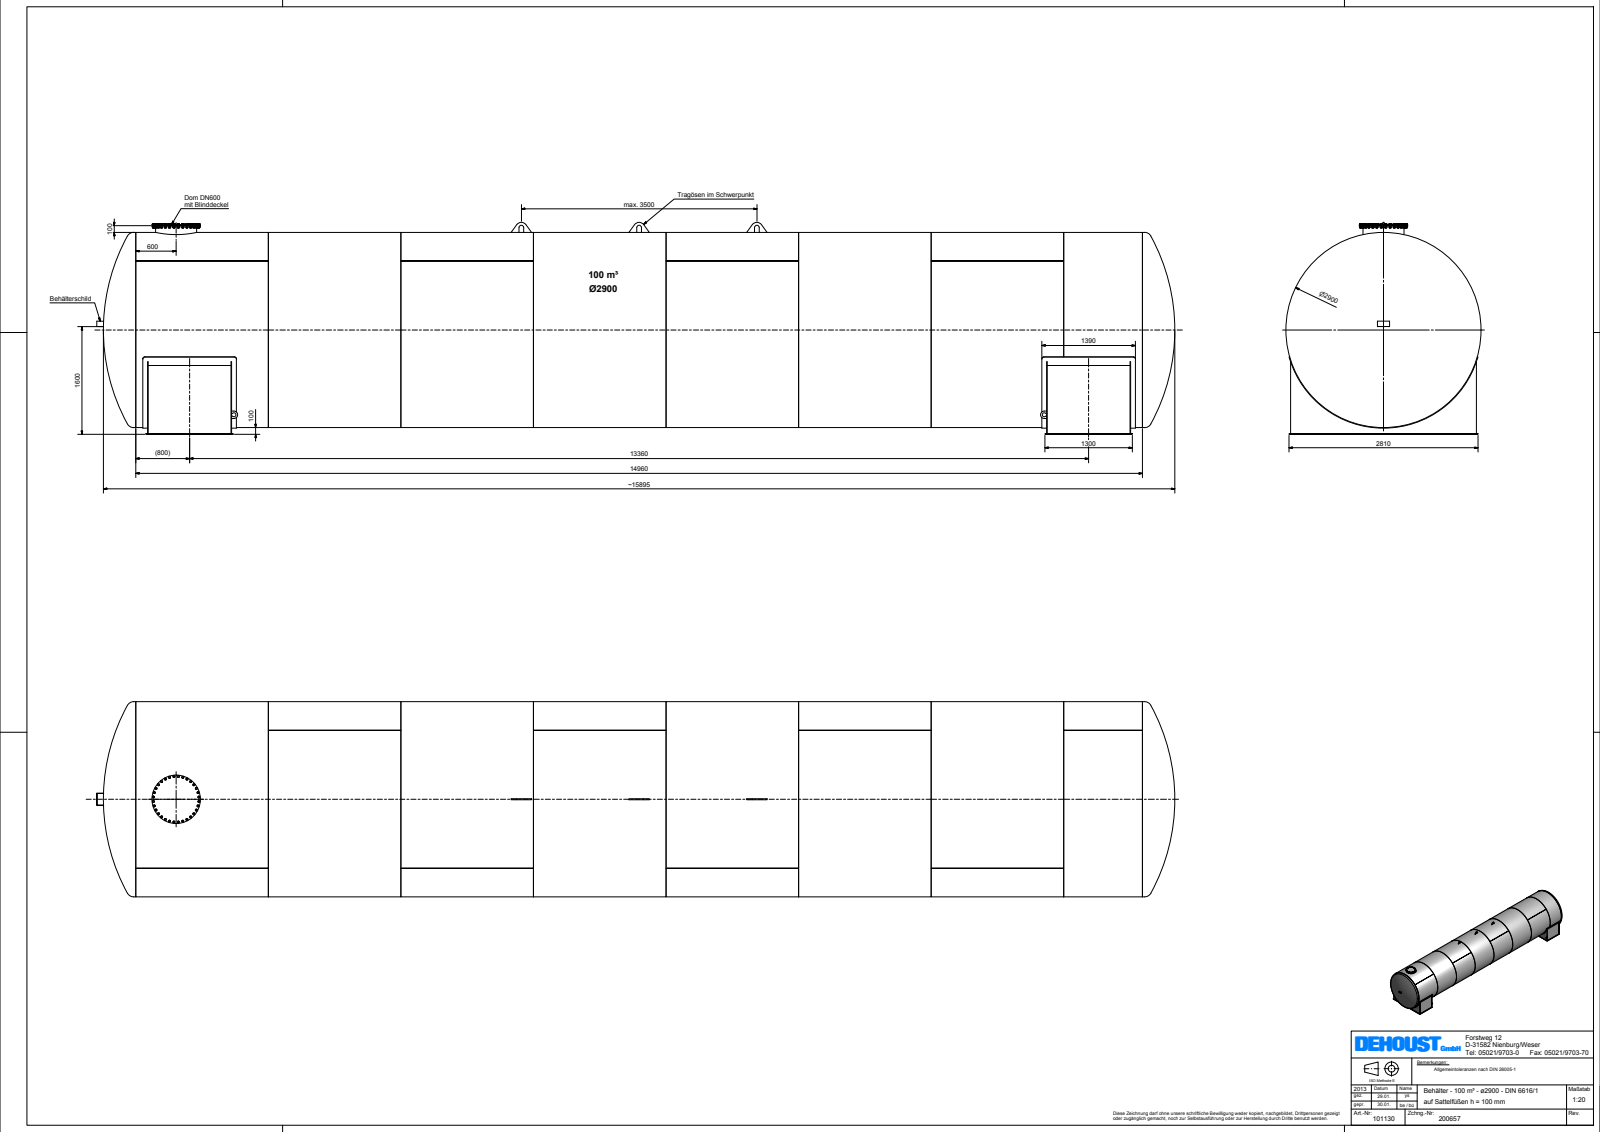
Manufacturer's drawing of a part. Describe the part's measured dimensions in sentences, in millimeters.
The part is named "Beh\\S\\dlter_6616_E_2900_100_100_KV". Its 3-D file was written by "Autodesk Inventor 2012 (AUTOMOTIVE_DESIGN)". It is 5 solids with 1169 faces: 698 planar, 179 cylindrical and 292 other. Overall it measures 16020.62 by 3150 by 2900 millimeters. Its volume is 5 318 000 000 cubic millimeters and its surface area 334 600 000 square millimeters. Round holes: 1 of diameter 598, 1 of diameter 2882. Round bosses or shafts: 32 of diameter 24.8, 32 of diameter 18, 32 of diameter 16.65, 1 of diameter 2900, 1 of diameter 720, 1 of diameter 660, 1 of diameter 610. Partial cylindrical surfaces (rounded edges, fillets, slot ends): 8 of radius 30, 3 of radius 35, 3 of radius 85, 2 of radius 29.73, 2 of radius 55, 1 of radius 1459. The main face-to-face distances are 9, 14960, 2711, 13360, 1239, 2720, 2702, 176, 14784, 1424.
